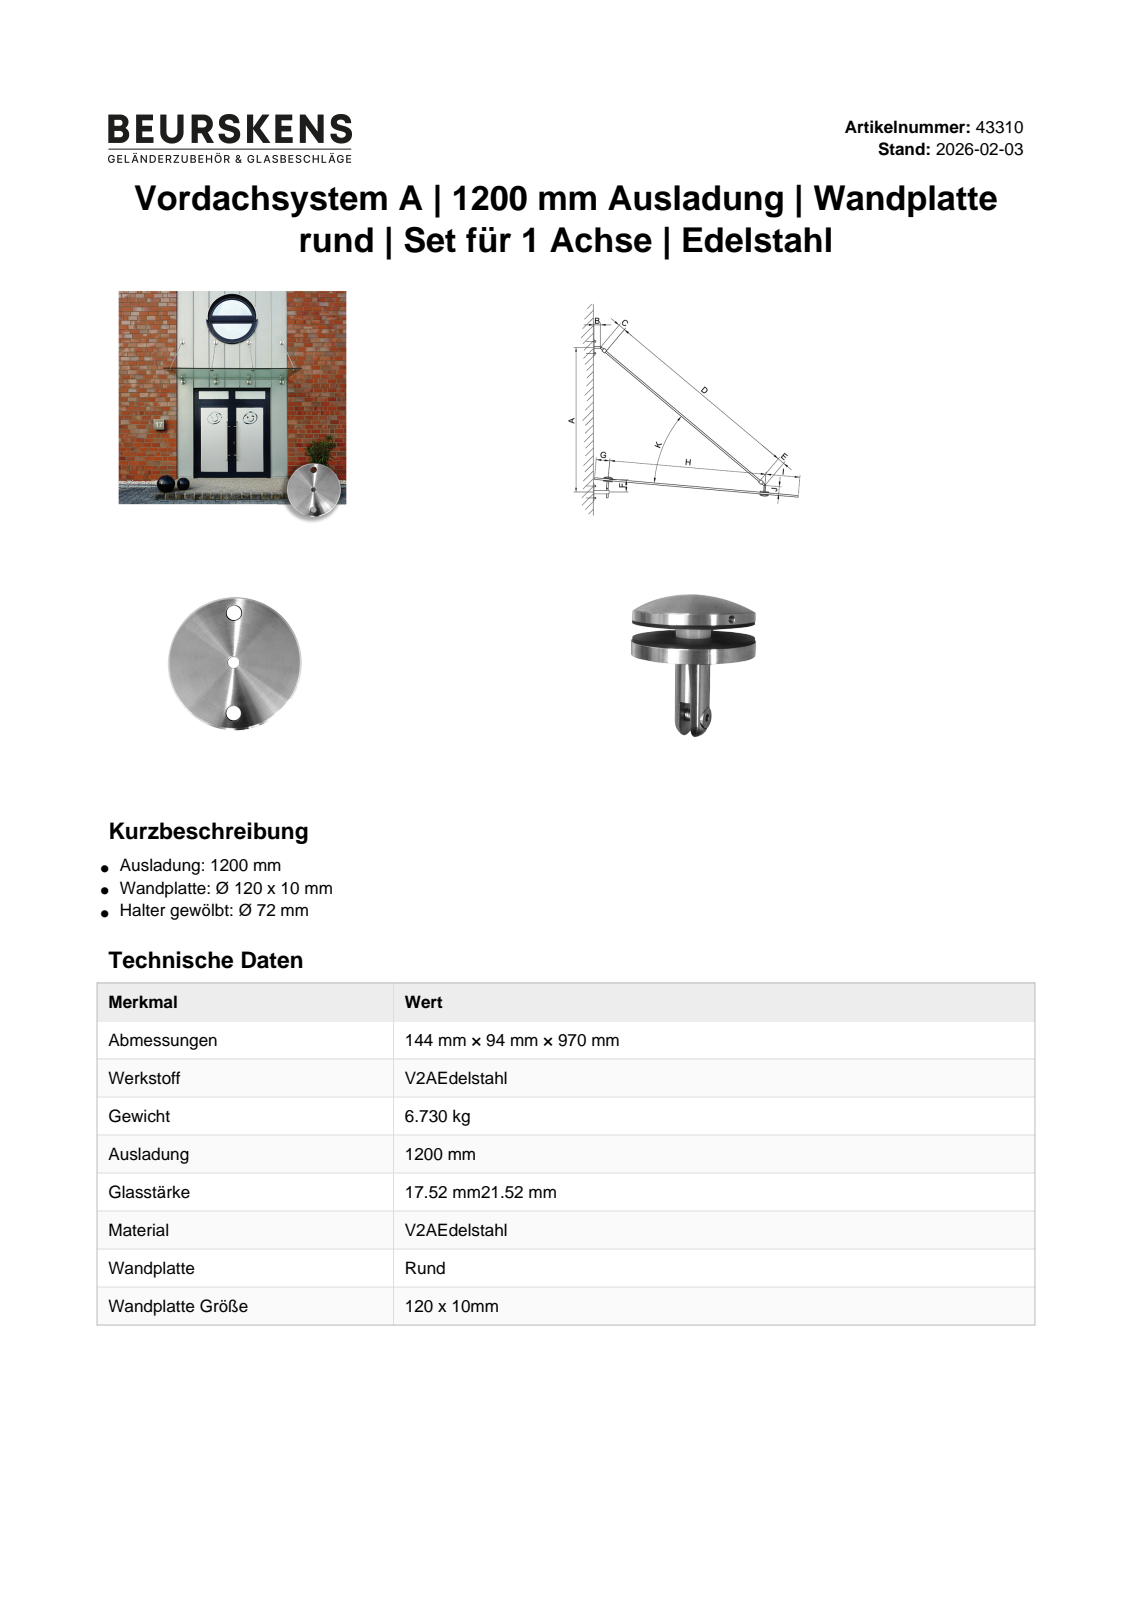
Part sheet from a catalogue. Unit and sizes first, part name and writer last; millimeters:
Units: millimetres
Overall size (bounding box): 1048.53 × 1000 × 120
Round holes (diameter × count): ⌀10 ×12, ⌀5 ×5, ⌀10.5 ×4, ⌀13 ×4, ⌀14 ×4, ⌀14.2 ×4, ⌀8 ×3, ⌀8.5 ×3, ⌀12.5 ×3, ⌀3 ×2, ⌀18 ×2, ⌀21 ×1
Round bosses / shafts (diameter × count): ⌀20 ×7, ⌀72 ×4, ⌀70 ×4, ⌀12 ×3, ⌀120 ×2, ⌀24 ×2, ⌀20.2 ×2, ⌀16 ×2
Main face-to-face distances: 10, 2, 8.26, 29.53, 19.53, 10.26, 27.53, 21.27, 19.27, 21.53
Hole centre spacings: 919.91, 919.9, 45, 0.75, 880, 32, 90, 835
Volume: 766 722 mm³ · Surface area: 252 271 mm²
Bodies: 31 solids, 311 faces (169 planar, 96 cylindrical, 46 other)
Part name (STEP PRODUCT): 43310; 41122; 41785; DIN 7991 - M10x12 (+8 more)
STEP written by: Autodesk Inventor 2022 (AUTOMOTIVE_DESIGN)
